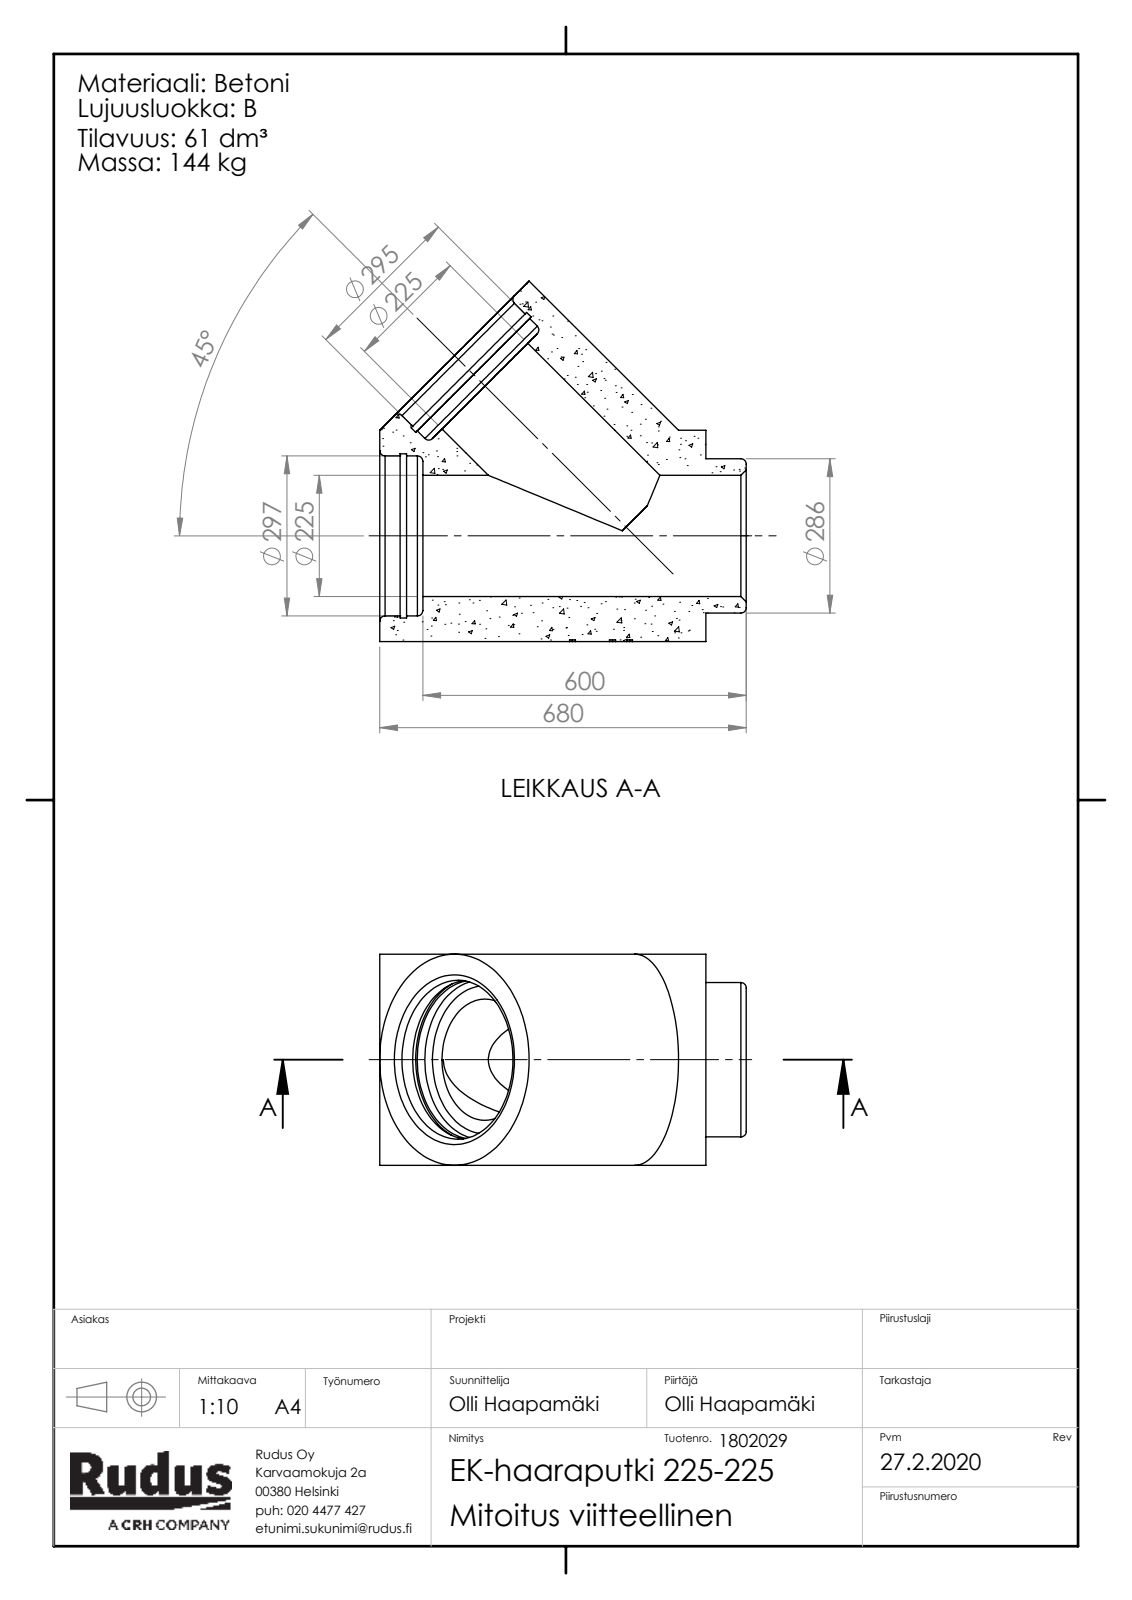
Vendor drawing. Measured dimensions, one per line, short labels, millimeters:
name: EK-osa-haararunko; Rudus 1802029 EK-haaraputki 225-225
written by: SolidWorks 2019 (CONFIG_CONTROL_DESIGN)
unit: mm
bodies: 1 solid, 119 faces (39 planar, 30 cylindrical, 50 other)
size: 680 × 669.19 × 392
volume: 61 360 000 mm³; area: 1 905 000 mm²
holes: 2× ⌀225, 1× ⌀295, 1× ⌀297, 1× ⌀303, 1× ⌀305
bosses: 1× ⌀392, 1× ⌀286.4
rounds: 1× R193
face distances: 605, 80, 525, 79.99, 680, 600, 75, 42, 12, 30
